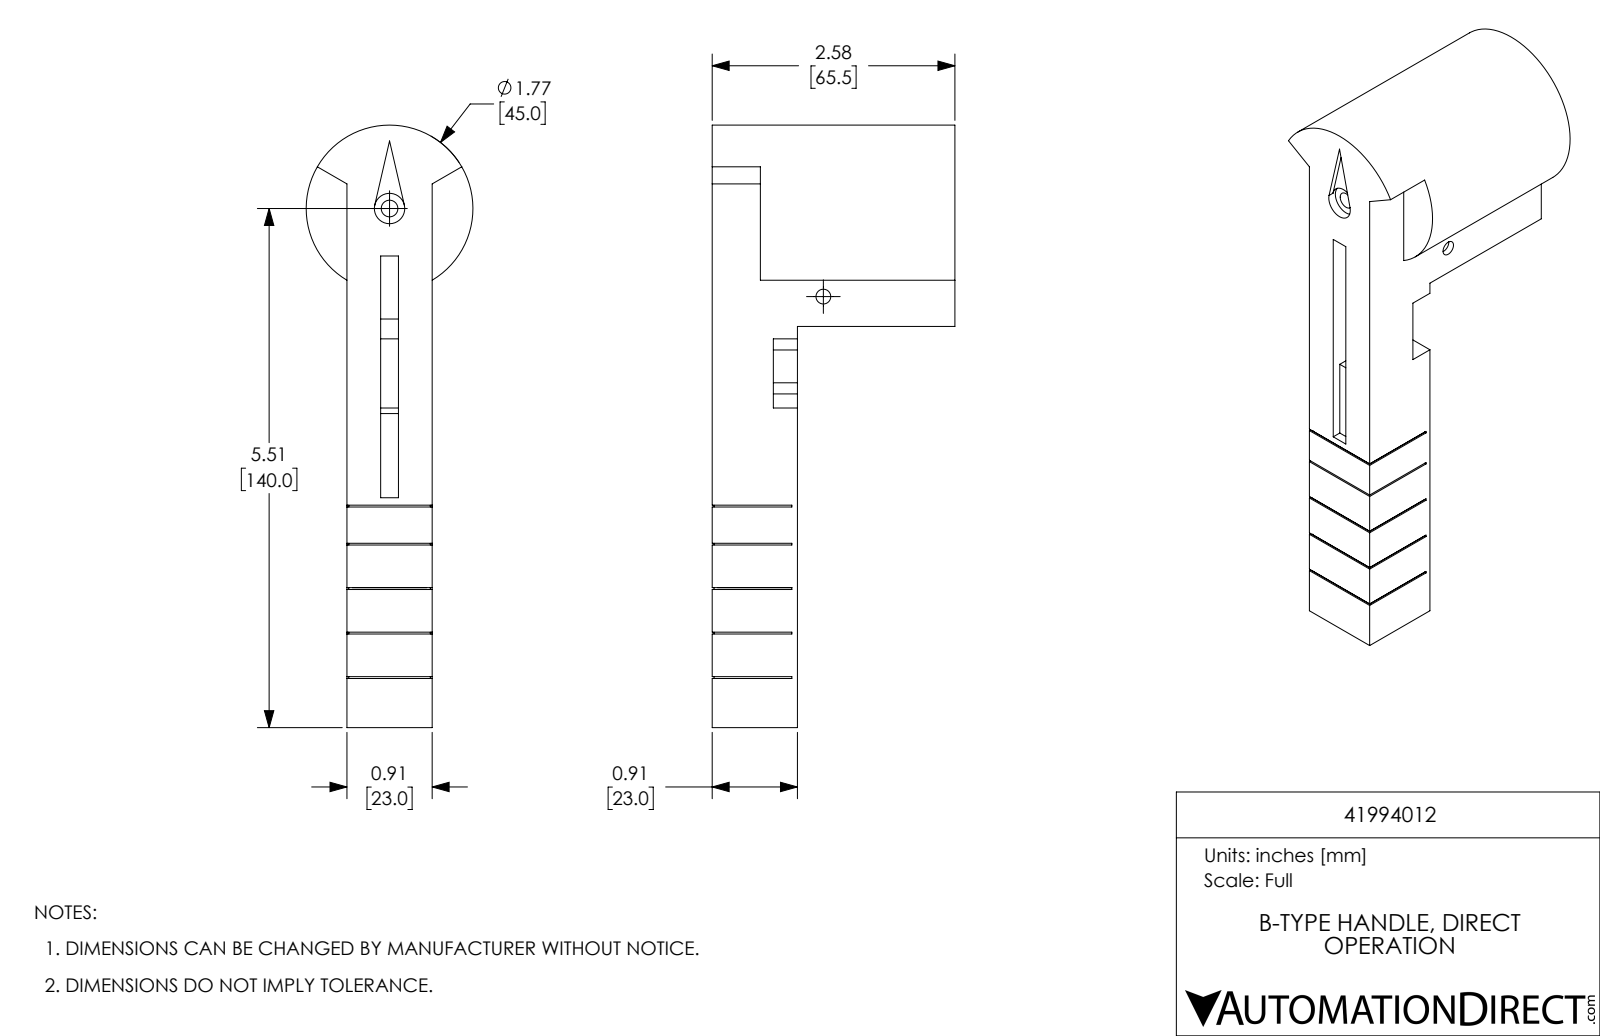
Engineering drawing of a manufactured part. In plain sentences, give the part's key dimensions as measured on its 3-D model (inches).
The part is named "41994012". Its 3-D file was written by "SolidWorks 2017 (AUTOMOTIVE_DESIGN)". It is 1 solid with 162 faces: 142 planar, 16 cylindrical and 4 other. Overall it measures 6.398 by 2.579 by 1.772 inches. Its volume is 8.769 cubic inches and its surface area 55.51 square inches. Round holes: 1 of diameter 0.157, 1 of diameter 0.177, 1 of diameter 0.323. Round bosses or shafts: 1 of diameter 1.772. Partial cylindrical surfaces (rounded edges, fillets, slot ends): 3 of radius 0.02. The main face-to-face distances are 0.906, 0.358, 0.547, 0.394, 1.673, 0.189, 2.579, 0.079, 0.581, 0.472.
